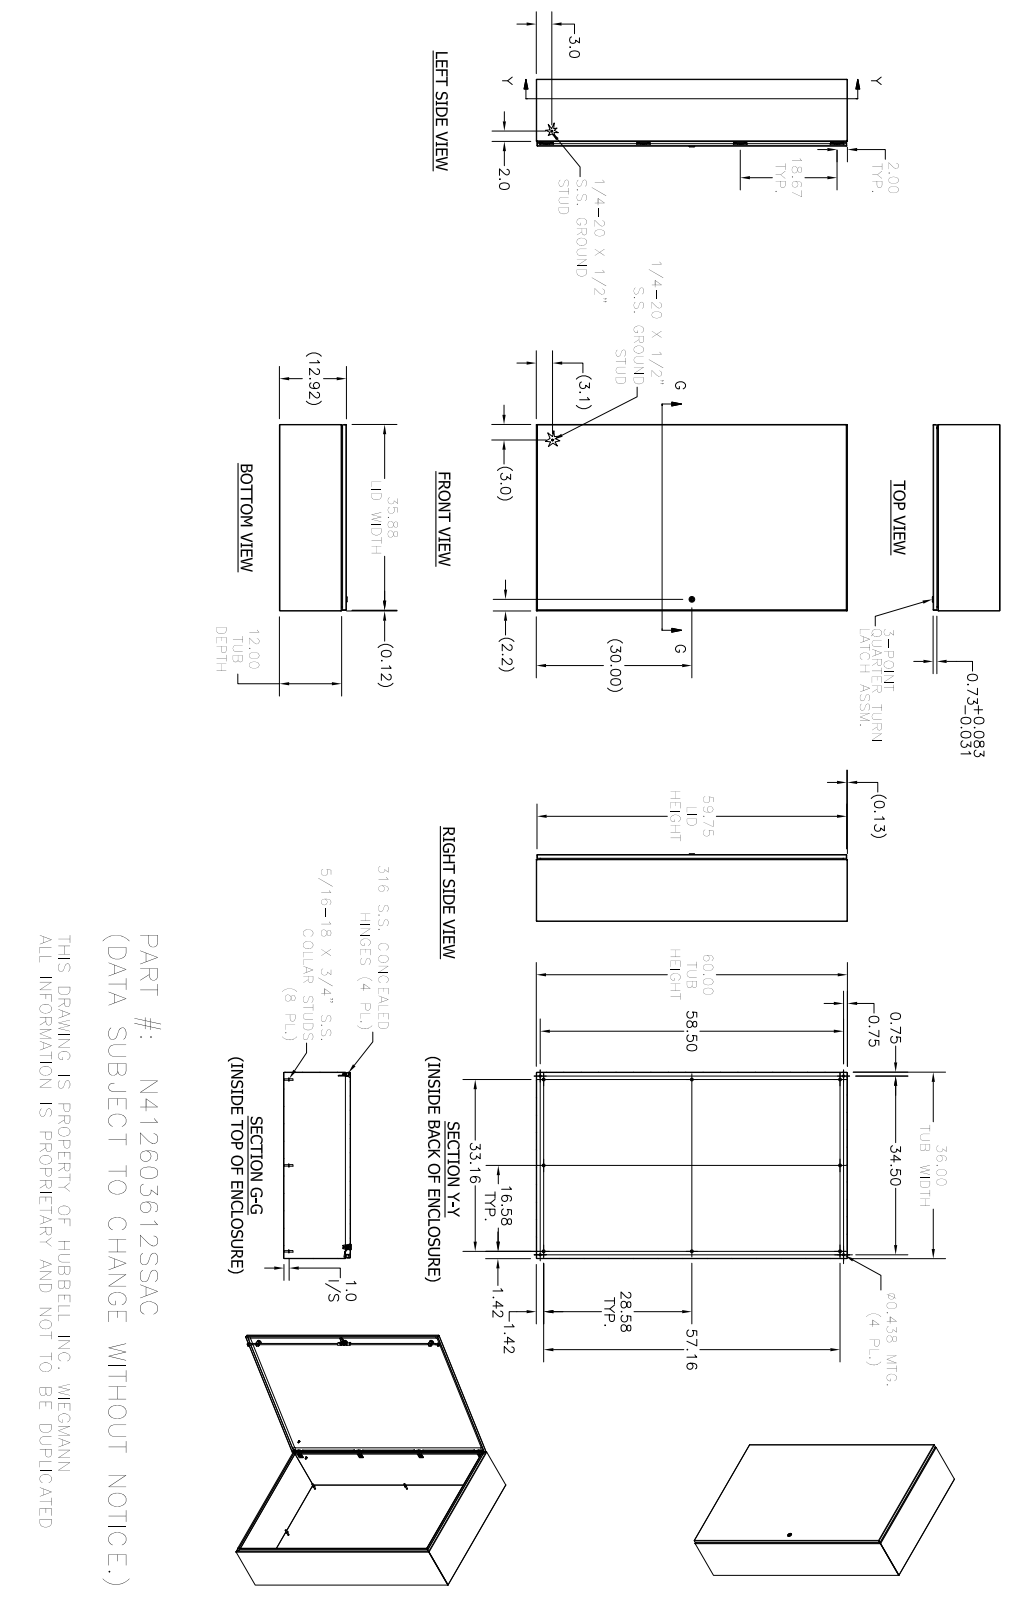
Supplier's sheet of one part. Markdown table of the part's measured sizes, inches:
| quantity | value |
| --- | --- |
| part name | N412603612SSACBTB; N4126012SSACLS; N4126012SSACRS; 388151 (+8 more) |
| STEP written by | Autodesk Inventor 2016 (AUTOMOTIVE_DESIGN) |
| units | inches |
| bodies | 82 solids, 2666 faces (979 planar, 994 cylindrical, 693 other) |
| overall size | 60 × 36 × 13.075 |
| volume | 555.8 in³ |
| surface area | 14 450 in² |
| round holes (diameter × count) | 0.093 × 8, 0.152 × 8, 0.167 × 8, 0.172 × 8, 0.187 × 8, 0.197 × 5, 0.156 × 4, 0.165 × 4, 0.437 × 4, 0.106 × 2, 0.16 × 2, 0.169 × 2 |
| round bosses / shafts (diameter × count) | 0.25 × 18, 0.563 × 8, 0.36 × 8, 0.32 × 8, 0.3 × 8, 0.275 × 8, 0.256 × 8, 0.164 × 8 |
| partial cylindrical surfaces (radius × count) | 0.05 × 50, 0.031 × 36, 0.016 × 34, 0.125 × 32, 0.012 × 30, 0.02 × 20, 0.105 × 18, 0.032 × 16 |
| main face-to-face distances | 0.074, 12.843, 12.769, 12.917, 35.926, 59.926, 35.852, 36, 59.852, 60 |
| hole center spacings | 18.667, 37.333, 18.667, 56, 37.333, 0.5, 0.656, 18.673 |
